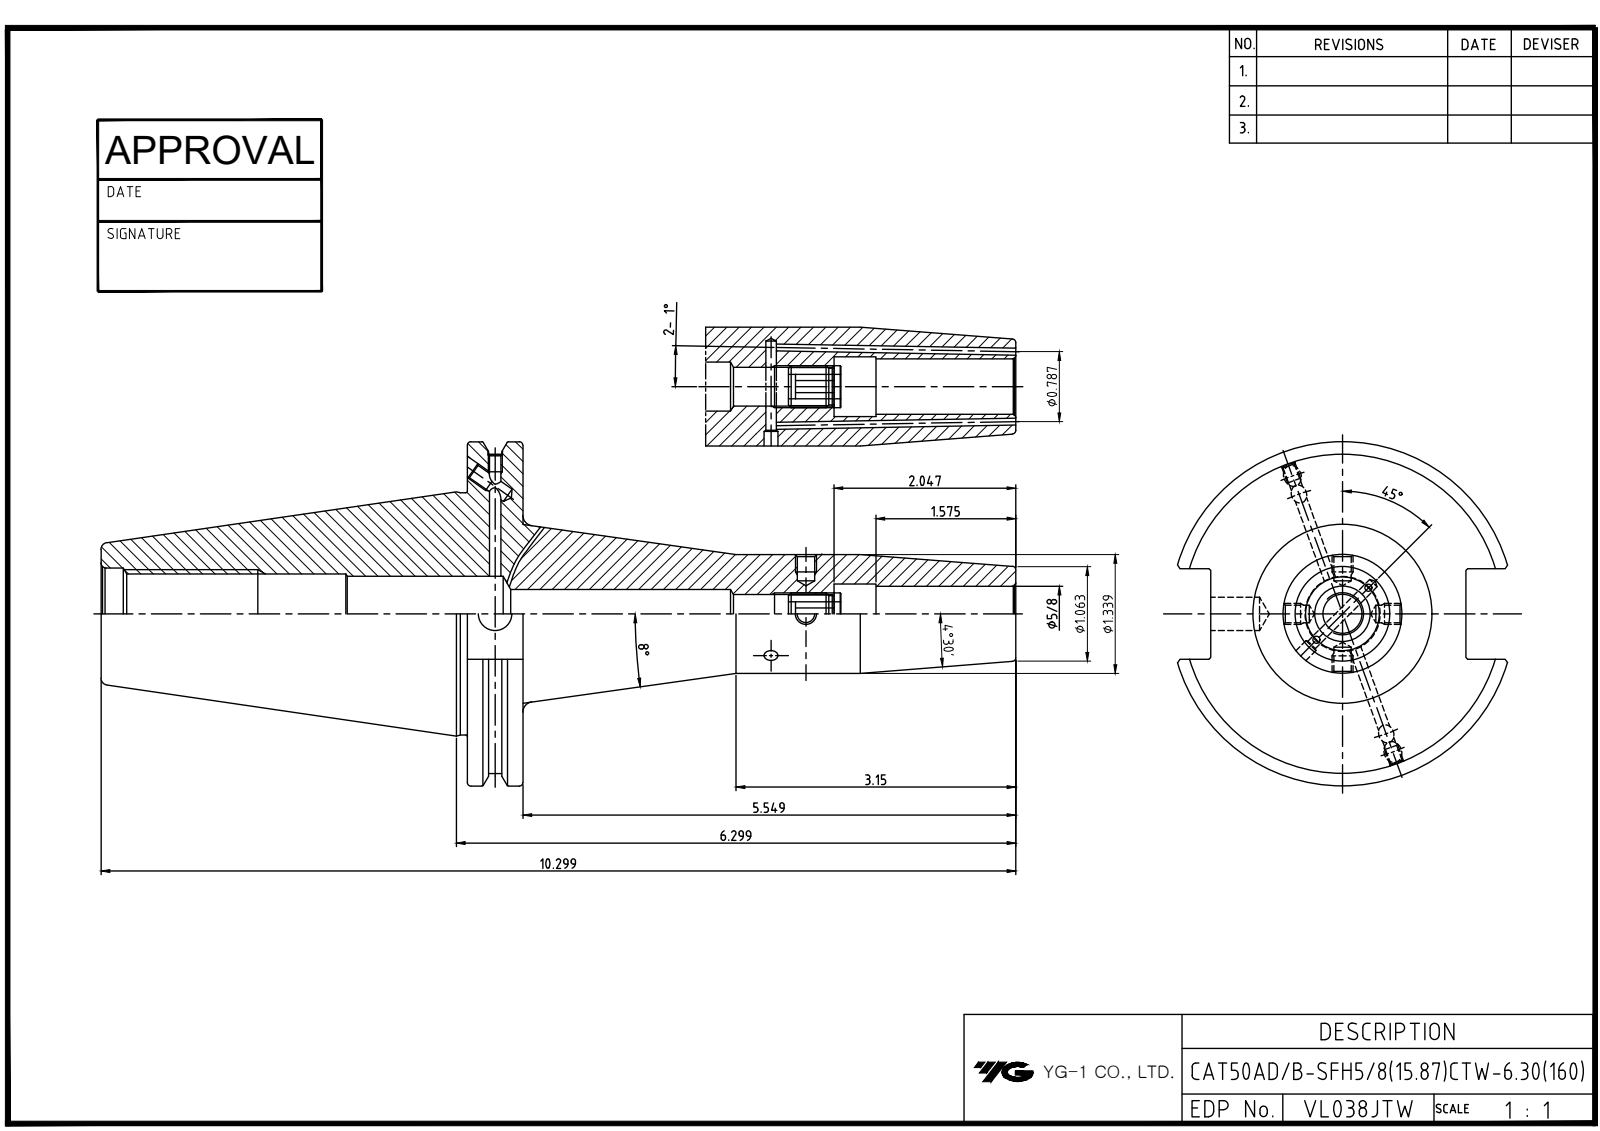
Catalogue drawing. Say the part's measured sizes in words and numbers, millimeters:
The part is named "CAT50_SHANK_20130708". Its 3-D file was written by "CREO PARAMETRIC BY PTC INC, 2018500 (CONFIG_CONTROL_DESIGN)". It is 1 solid with 102 faces: 30 planar, 30 cylindrical and 42 other. Overall it measures 261.75 by 98.42 by 94.43 millimeters. Its volume is 453 123 cubic millimeters and its surface area 67 845 square millimeters. Round holes: 1 of diameter 9.53, 1 of diameter 12, 1 of diameter 14, 1 of diameter 15.88, 1 of diameter 17.07, 1 of diameter 20.5, 1 of diameter 21, 1 of diameter 24, 1 of diameter 25, 1 of diameter 25.6. Round bosses or shafts: 1 of diameter 98.42, 1 of diameter 91.29, 1 of diameter 69.25, 1 of diameter 34.01. The main face-to-face distances are 15.9, 104.9, 120.8, 73.03, 25.7, 261.75, 156.85, 140.95, 110.99, 6.09.
